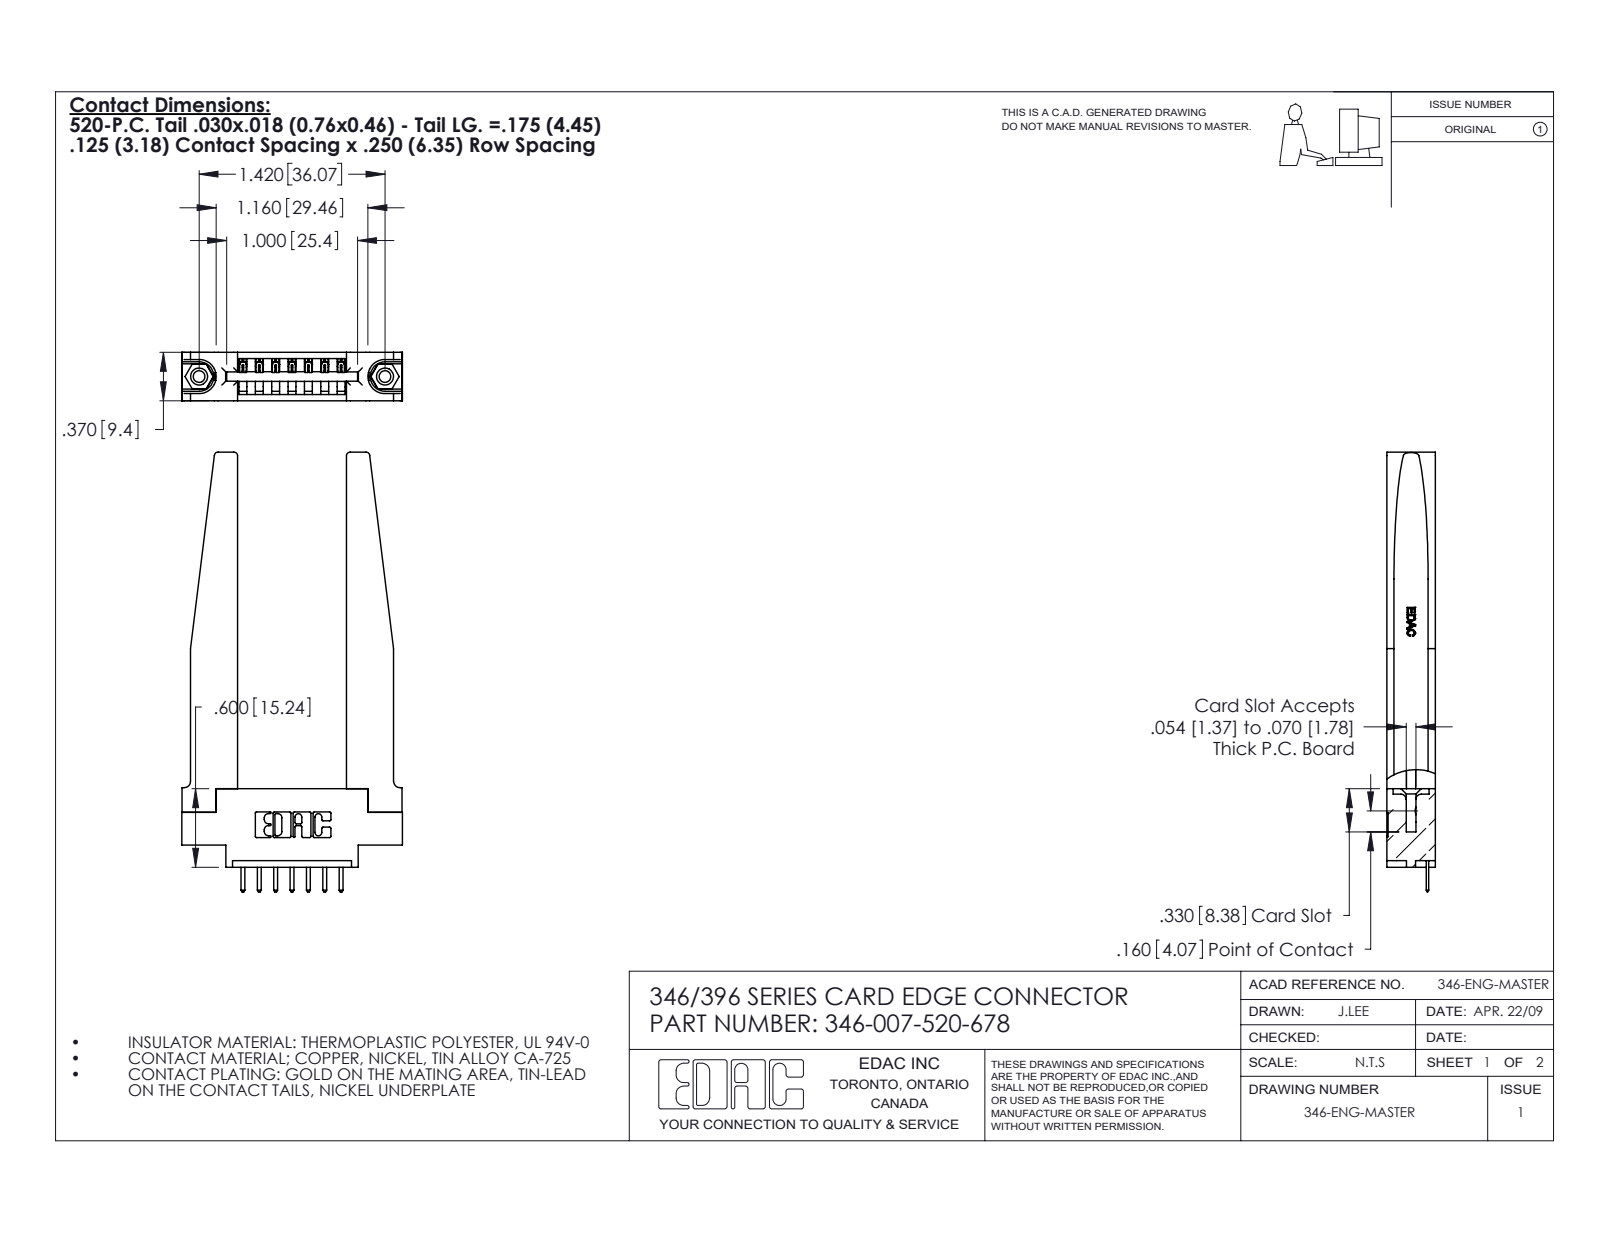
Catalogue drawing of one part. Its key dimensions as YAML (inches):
part_name: "346 Part_0.170 Offset - 0.156 Dia-TH; 346-220-078_345-220-078; 345-250-001_345-250-001-102; 346-007-520-678 (+1 more)"
step_written_by: "SolidWorks 2020 (CONFIG_CONTROL_DESIGN)"
units: inches
bodies: {solids: 12, faces: 808, planar: 530, cylindrical: 226, other: 52}
overall_size: [3.358, 1.685, 0.37]
volume: 0.645
surface_area: 16.84
round_holes:
  - {diameter: 0.089, count: 2}
  - {diameter: 0.125, count: 2}
  - {diameter: 0.156, count: 2}
  - {diameter: 0.064, count: 1}
round_bosses_or_shafts:
  - {diameter: 0.155, count: 2}
partial_cylinders:
  - {radius: 0.01, count: 22}
  - {radius: 0.01, count: 16}
  - {radius: 0.006, count: 14}
  - {radius: 0.03, count: 8}
  - {radius: 0.007, count: 6}
  - {radius: 0.031, count: 6}
  - {radius: 0.026, count: 3}
  - {radius: 0.031, count: 2}
face_to_face_distances: [0.37, 0.15, 0.22, 0.831, 0.25, 0.072, 0.148, 0.048, 0.322, 0.102]
hole_center_spacings: [0.246, 1.217, 1.42]
